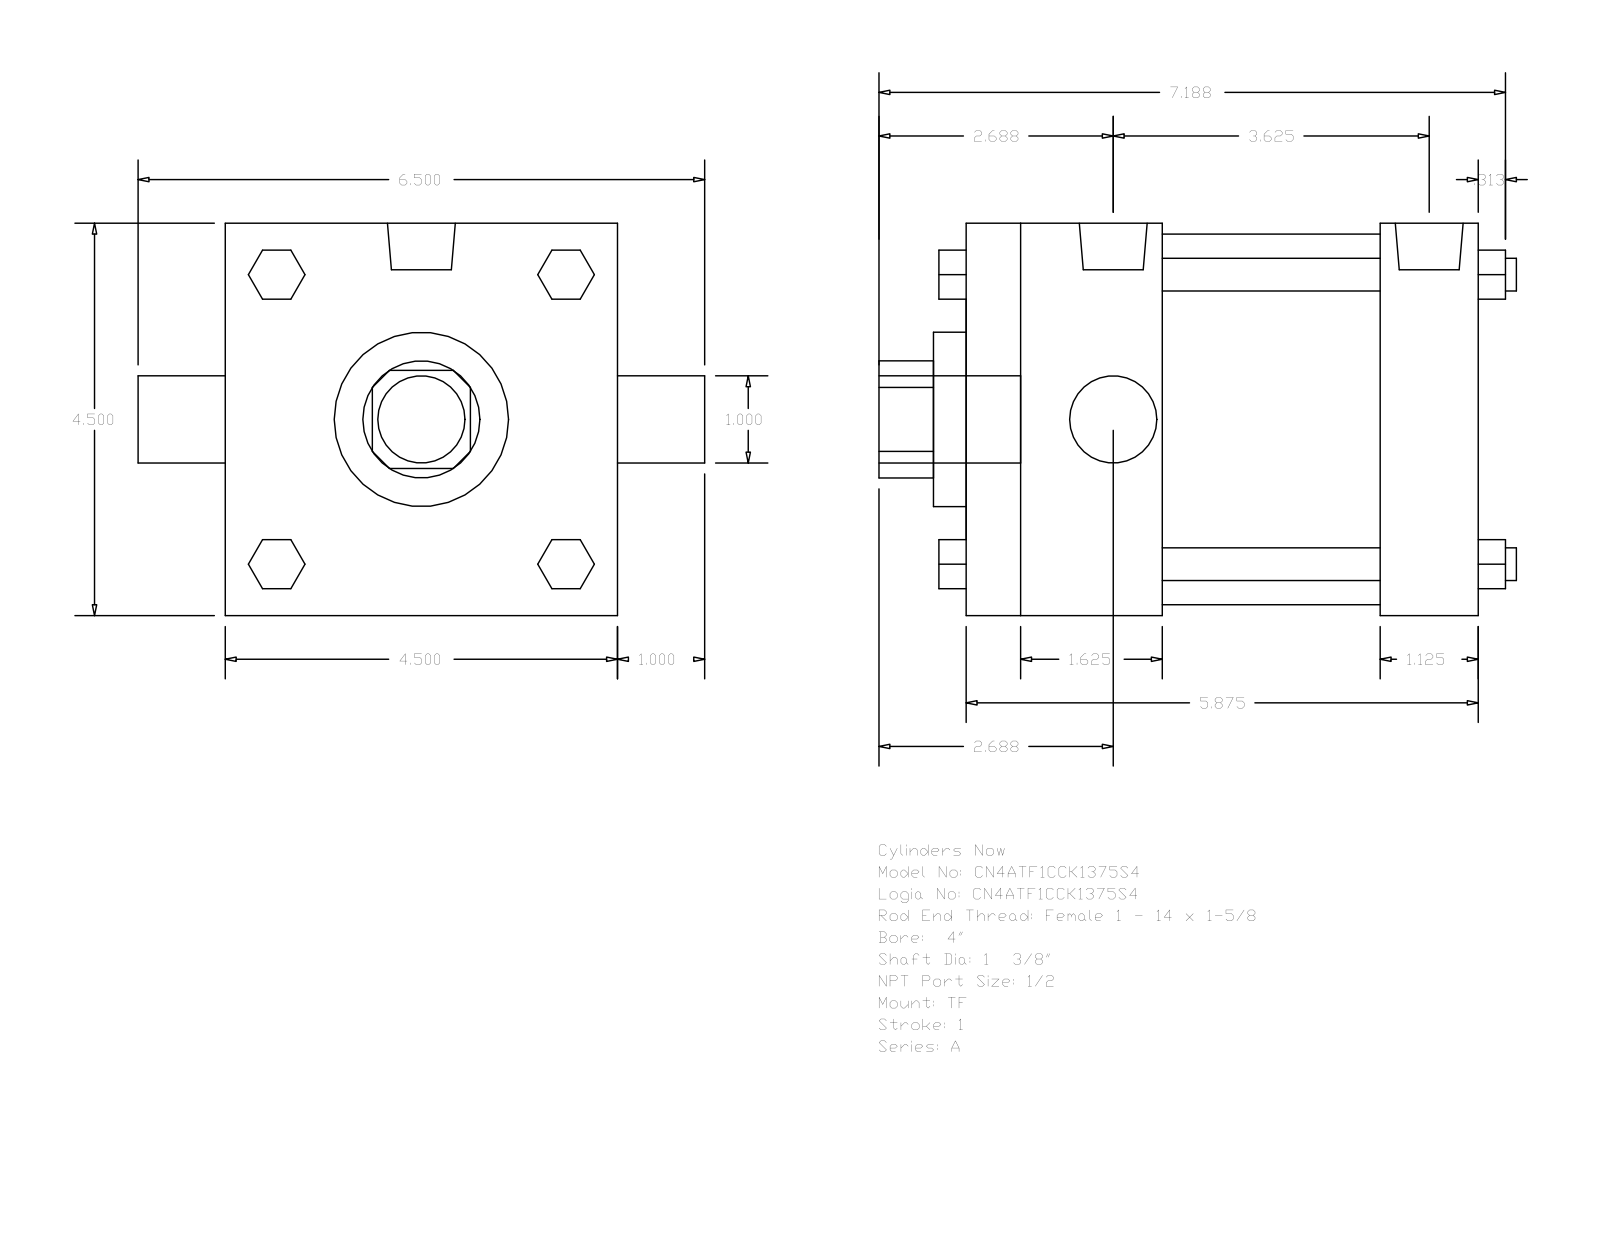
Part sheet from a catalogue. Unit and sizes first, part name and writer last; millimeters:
Units: millimetres
Overall size (bounding box): 185.74 × 165.1 × 114.3
Round holes (diameter × count): ⌀25.4 ×1, ⌀34.92 ×1, ⌀50.8 ×1, ⌀107.95 ×1
Round bosses / shafts (diameter × count): ⌀9.53 ×4, ⌀8.73 ×3, ⌀19.77 ×2, ⌀25.4 ×1
Partial cylindrical surfaces — rounded edges, fillets, slot ends (radius × count): R17.06 ×1
Main face-to-face distances: 114.3, 149.22, 28.57, 120.65, 57.15, 63.5, 92.07, 14.29, 25.4, 9.52
Bodies: 0 solids, 120 faces (92 planar, 28 cylindrical, 0 other)
Part name (STEP PRODUCT): A_TF__0400_1.375
STEP written by: GSSL Pune (CONFIG_CONTROL_DESIGN)
